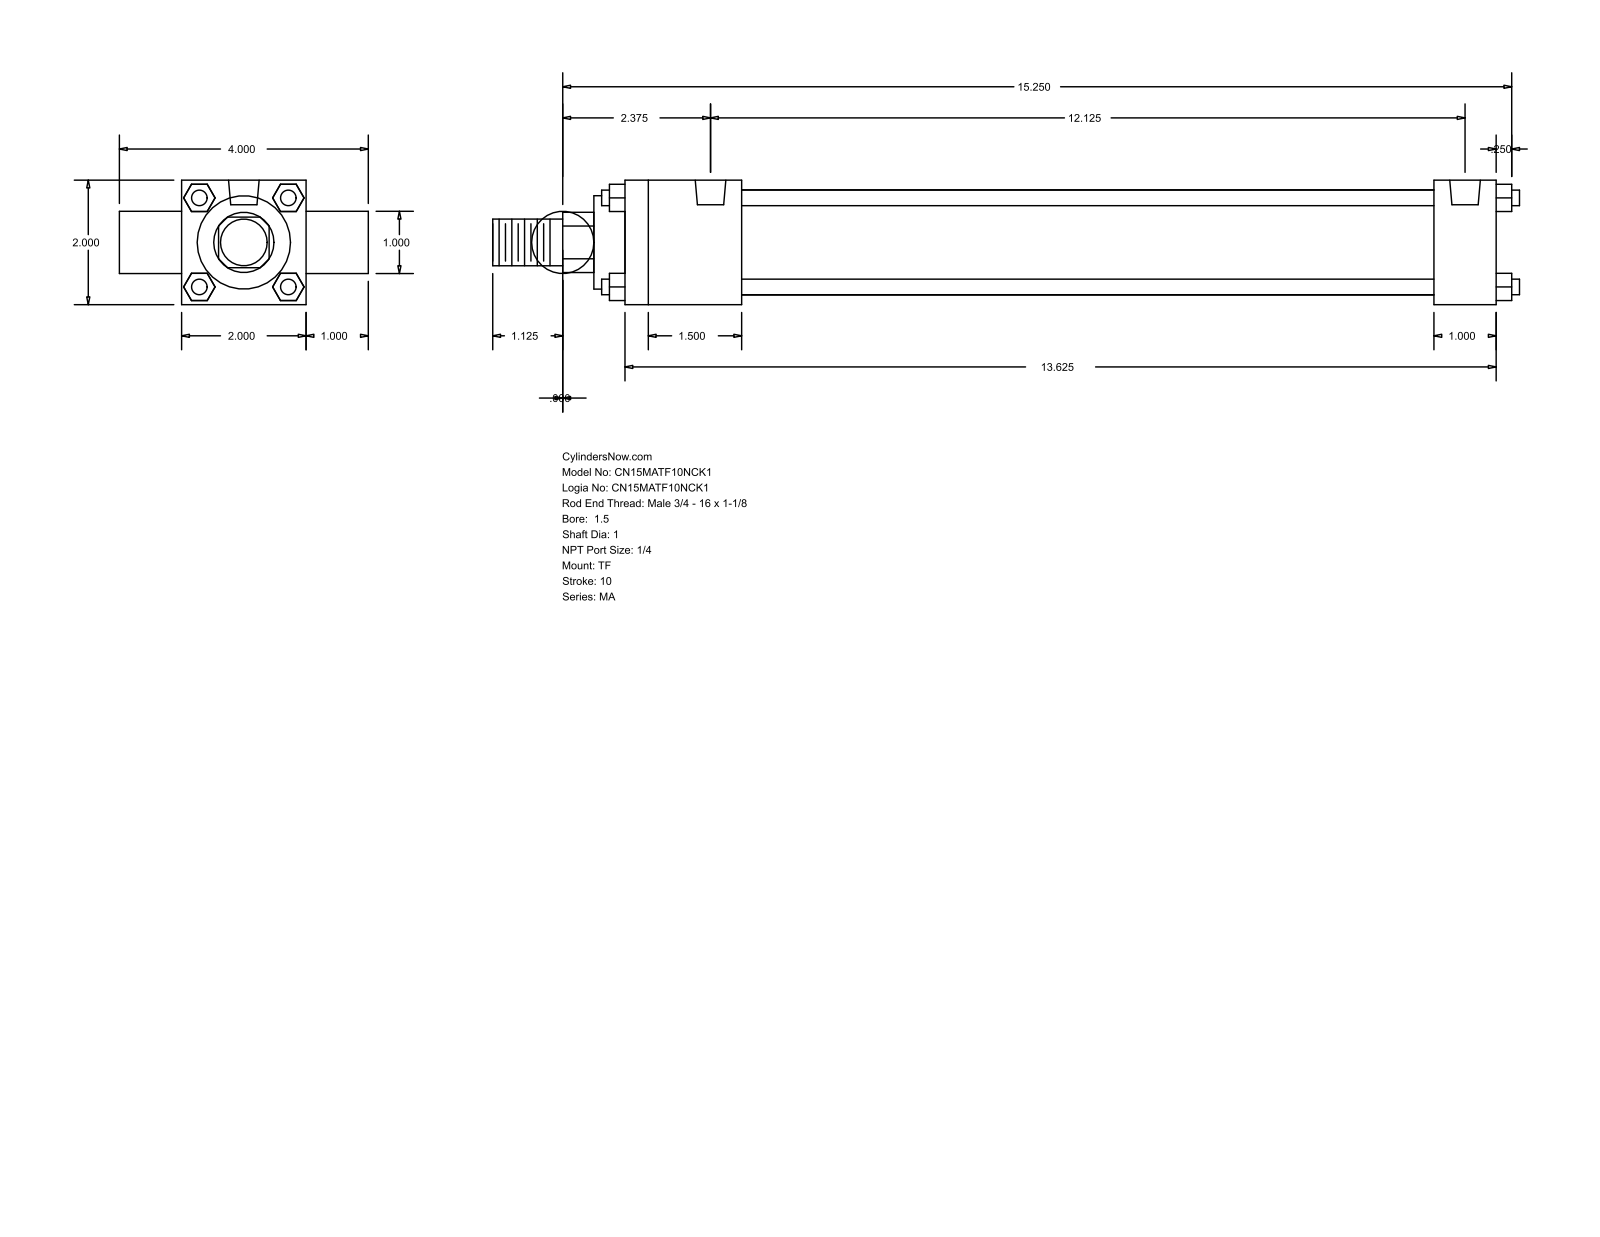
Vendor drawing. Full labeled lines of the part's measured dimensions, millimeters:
Part name (STEP PRODUCT): MA_TF__0150_1
STEP written by: GSSL Pune (CONFIG_CONTROL_DESIGN)
Units: millimetres
Bodies: 0 solids, 120 faces (92 planar, 28 cylindrical, 0 other)
Overall size (bounding box): 419.1 × 101.6 × 50.8
Round holes (diameter × count): ⌀7.94 ×3, ⌀12.49 ×2
Round bosses / shafts (diameter × count): ⌀6.35 ×4, ⌀25.4 ×2, ⌀42.93 ×1, ⌀38.1 ×1, ⌀19.05 ×1
Partial cylindrical surfaces — rounded edges, fillets, slot ends (radius × count): R12.29 ×1
Main face-to-face distances: 50.8, 25.4, 355.6, 76.2, 6.35, 47.63, 330.2, 282.57, 307.97, 368.3
Hole centre spacings: 307.97
